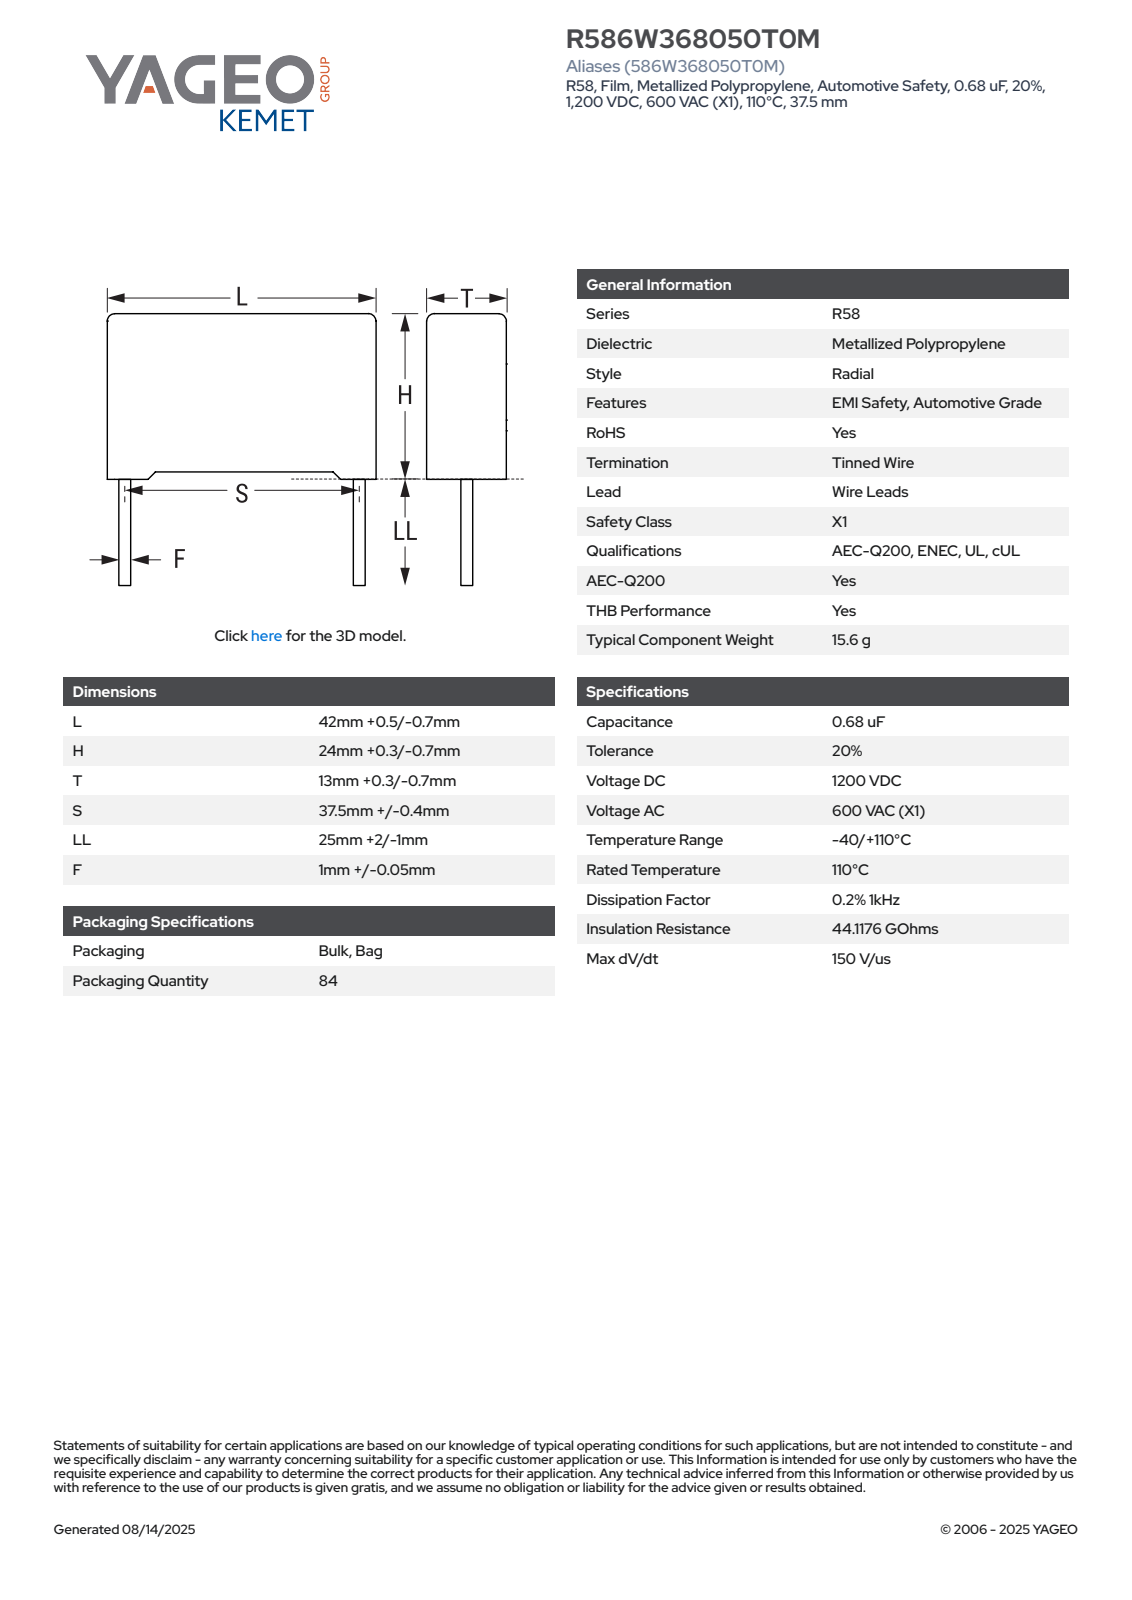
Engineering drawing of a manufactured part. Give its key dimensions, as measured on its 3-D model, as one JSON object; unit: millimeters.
{"part_name": "CFR_RB2_42X24X13_L42.5H24.3T13.3S37.5LL27F1.05", "step_written_by": "SolidWorks 2021 (AUTOMOTIVE_DESIGN)", "units": "millimeters", "bodies": {"solids": 4, "faces": 85, "planar": 77, "cylindrical": 8, "other": 0}, "overall_size": [51.3, 42.5, 13.3], "volume_mm3": 13358, "surface_area_mm2": 4108, "round_bosses_or_shafts": [[1.05, 2]], "partial_cylinders_radius": [[0.5, 4]], "face_to_face_distances": [13.3, 23.46, 42.5, 23.55, 0.75, 0.84, 24.3, 13.31, 1.42, 41.08]}
